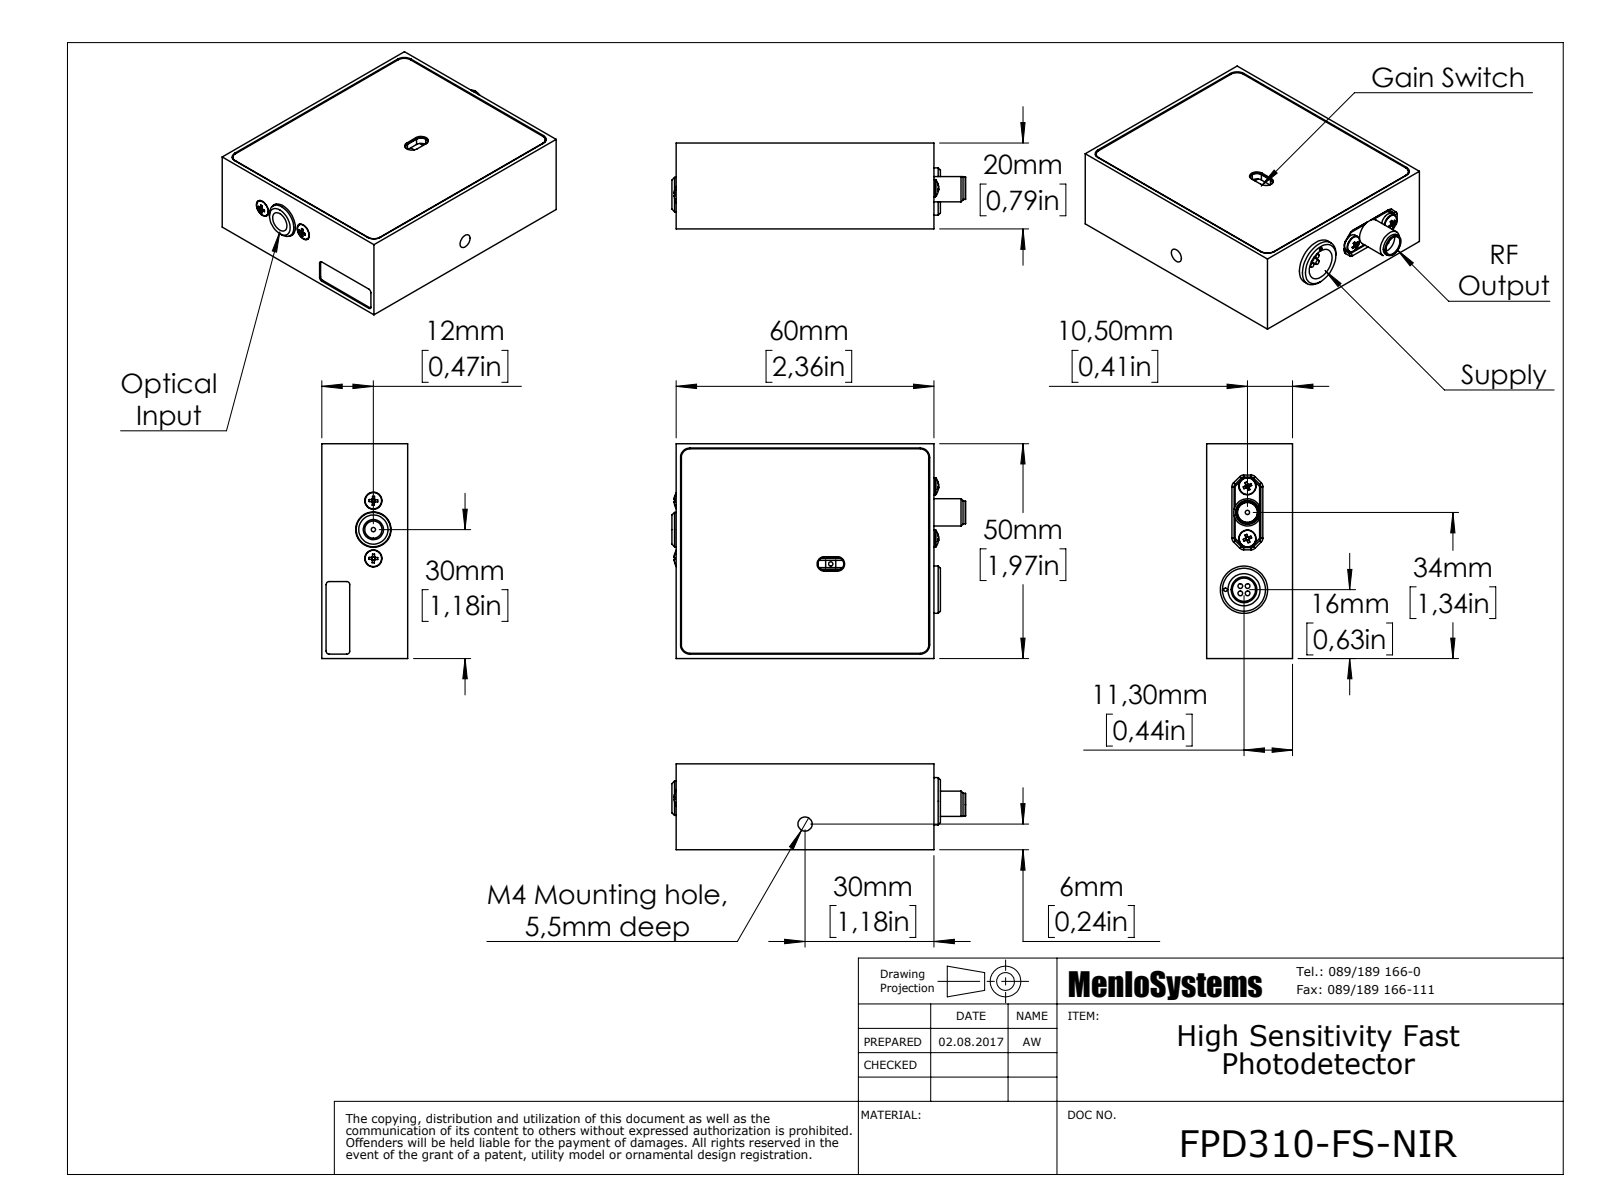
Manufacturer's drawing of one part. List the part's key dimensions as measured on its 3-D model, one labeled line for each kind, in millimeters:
Part name (STEP PRODUCT): FPD310-FS-NIR_170721
STEP written by: SolidWorks 2016 (AUTOMOTIVE_DESIGN)
Units: millimetres
Bodies: 22 solids, 1069 faces (457 planar, 288 cylindrical, 324 other)
Overall size (bounding box): 68.4 × 50 × 20
Volume: 38 516 mm³ · Surface area: 28 248 mm²
Round holes (diameter × count): ⌀1.6 ×23, ⌀4 ×13, ⌀2.2 ×10, ⌀2.6 ×2, ⌀0.8 ×1, ⌀1 ×1, ⌀3.2 ×1, ⌀3.3 ×1, ⌀4.6 ×1, ⌀4.7 ×1, ⌀7.5 ×1, ⌀8.25 ×1
Round bosses / shafts (diameter × count): ⌀2 ×14, ⌀3.8 ×12, ⌀1.1 ×4, ⌀0.5 ×3, ⌀4 ×2, ⌀11 ×1, ⌀9.6 ×1, ⌀9 ×1
Partial cylindrical surfaces — rounded edges, fillets, slot ends (radius × count): R2.2 ×26, R0.7 ×8, R0.8 ×8, R2 ×8, R1.4 ×4, R1.5 ×2, R1.7 ×2, R8 ×1
Main face-to-face distances: 1.5, 19.55, 0.35, 18.05, 1.85, 19.9, 6.5, 7, 50, 12.9
Hole centre spacings: 4.21, 9.27, 10.5, 14.96, 16.5, 19.36, 20, 21.82
